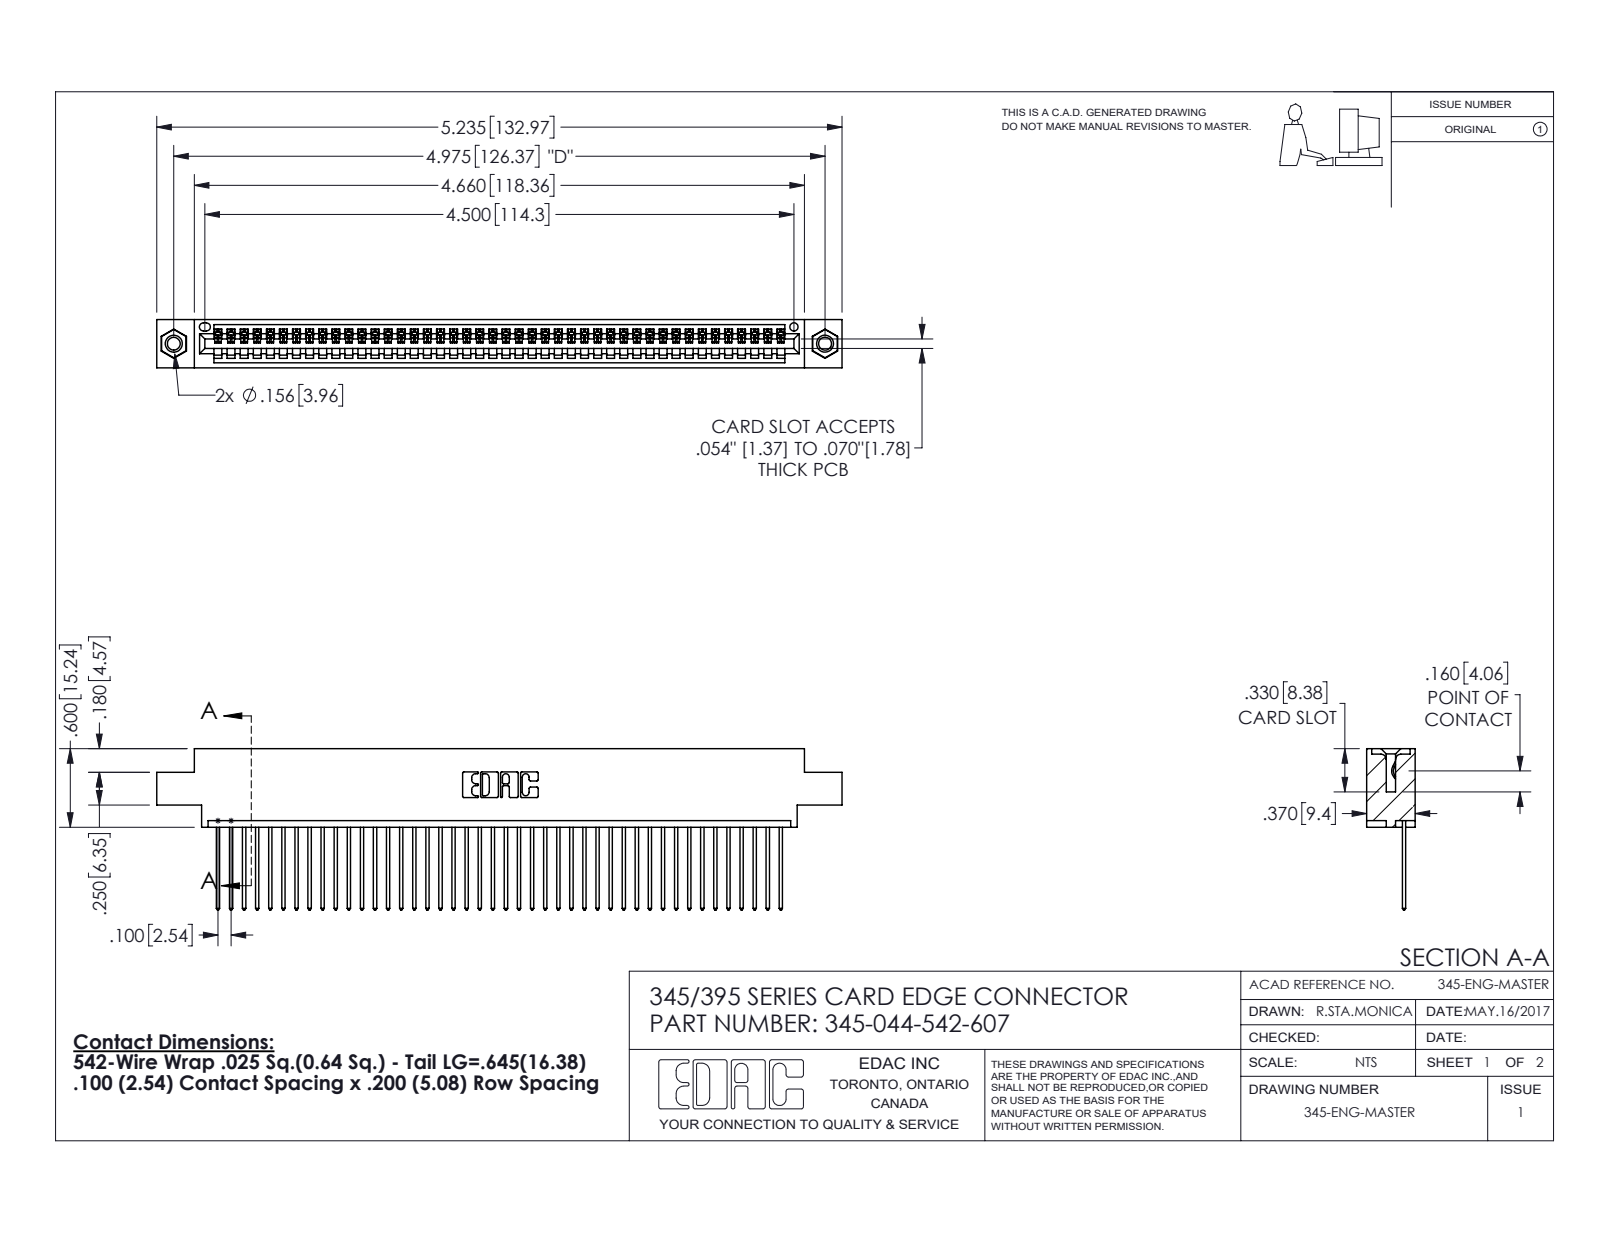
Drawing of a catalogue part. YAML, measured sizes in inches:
part_name: "345-250-001_345-250-005-103; 345-044-542-607; 345-292-001_345-293-142; 345 Part_0.170 Offset - 0.156 Dia-TI"
step_written_by: "SolidWorks 2016 (CONFIG_CONTROL_DESIGN)"
units: inches
bodies: {solids: 47, faces: 2742, planar: 1876, cylindrical: 850, other: 16}
overall_size: [5.235, 1.232, 0.37]
volume: 0.77
surface_area: 27.24
round_holes:
  - {diameter: 0.098, count: 2}
  - {diameter: 0.125, count: 2}
  - {diameter: 0.156, count: 2}
  - {diameter: 0.064, count: 1}
round_bosses_or_shafts:
  - {diameter: 0.155, count: 2}
partial_cylinders:
  - {radius: 0.006, count: 88}
  - {radius: 0.01, count: 88}
  - {radius: 0.01, count: 22}
  - {radius: 0.007, count: 6}
  - {radius: 0.031, count: 6}
  - {radius: 0.026, count: 3}
  - {radius: 0.031, count: 2}
  - {radius: 0.04, count: 2}
face_to_face_distances: [0.072, 0.298, 0.37, 0.098, 0.272, 0.025, 0.2, 0.225, 0.175, 0.149]
hole_center_spacings: [0.27, 4.739, 4.975]
